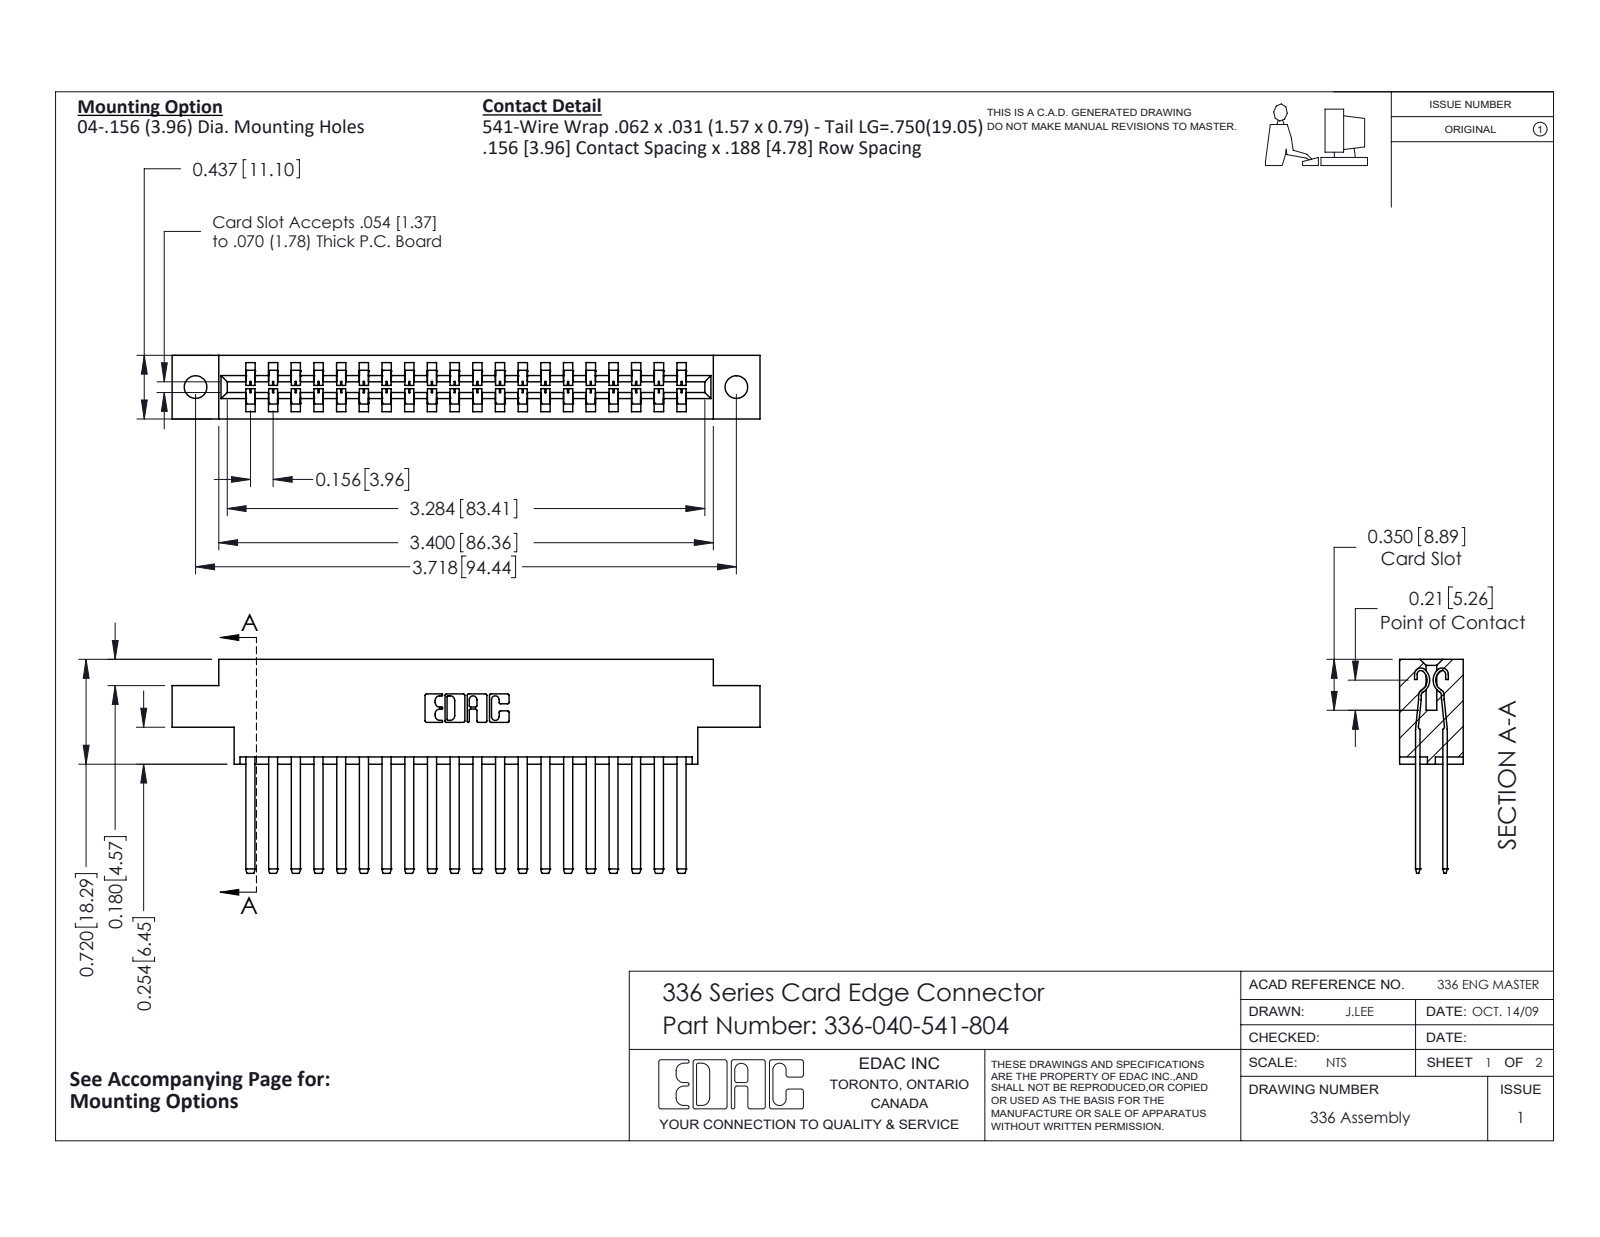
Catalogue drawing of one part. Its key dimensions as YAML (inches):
part_name: "336-040-541-804; 336 Part_Offset - .156 Dia - TH; 336-290-001_336-290-541"
step_written_by: "SolidWorks 2020 (CONFIG_CONTROL_DESIGN)"
units: inches
bodies: {solids: 41, faces: 1798, planar: 1114, cylindrical: 684, other: 0}
overall_size: [4.041, 1.47, 0.437]
volume: 0.918
surface_area: 28.94
round_holes:
  - {diameter: 0.156, count: 2}
partial_cylinders:
  - {radius: 0.004, count: 80}
  - {radius: 0.056, count: 40}
  - {radius: 0.01, count: 22}
  - {radius: 0.007, count: 6}
  - {radius: 0.031, count: 6}
  - {radius: 0.022, count: 4}
  - {radius: 0.04, count: 4}
  - {radius: 0.026, count: 3}
face_to_face_distances: [0.188, 0.328, 0.14, 0.297, 0.109, 0.031, 0.437, 0.033, 0.156, 0.181]
hole_center_spacings: [3.718]
